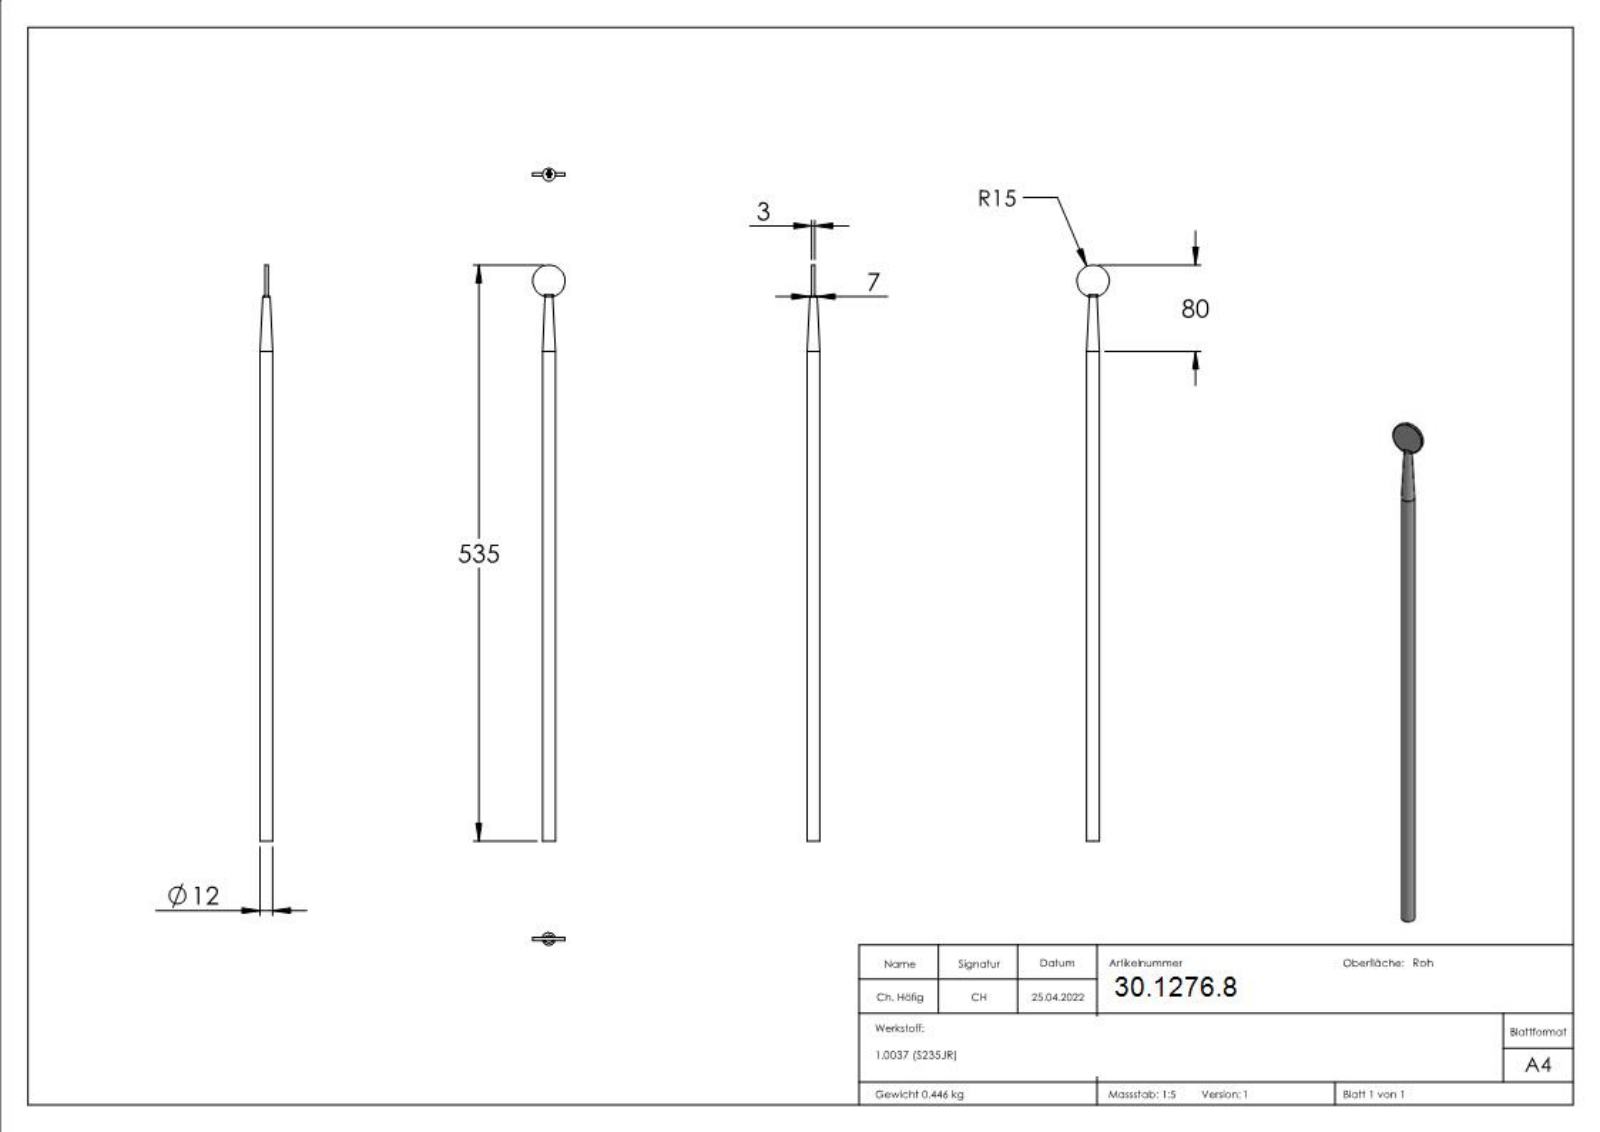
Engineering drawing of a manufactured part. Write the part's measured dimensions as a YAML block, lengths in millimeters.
part_name: "1444"
step_written_by: "SolidWorks 2018 (CONFIG_CONTROL_DESIGN)"
units: millimeters
bodies: {solids: 1, faces: 220, planar: 143, cylindrical: 4, other: 73}
overall_size: [535, 30, 12]
volume: 57238
surface_area: 20489
round_bosses_or_shafts:
  - {diameter: 30, count: 1}
  - {diameter: 12, count: 1}
partial_cylinders:
  - {radius: 2, count: 2}
face_to_face_distances: [3, 0.5, 2.21, 1.62, 0.34, 0.32, 2.45, 2.2, 2.24, 0.83]
